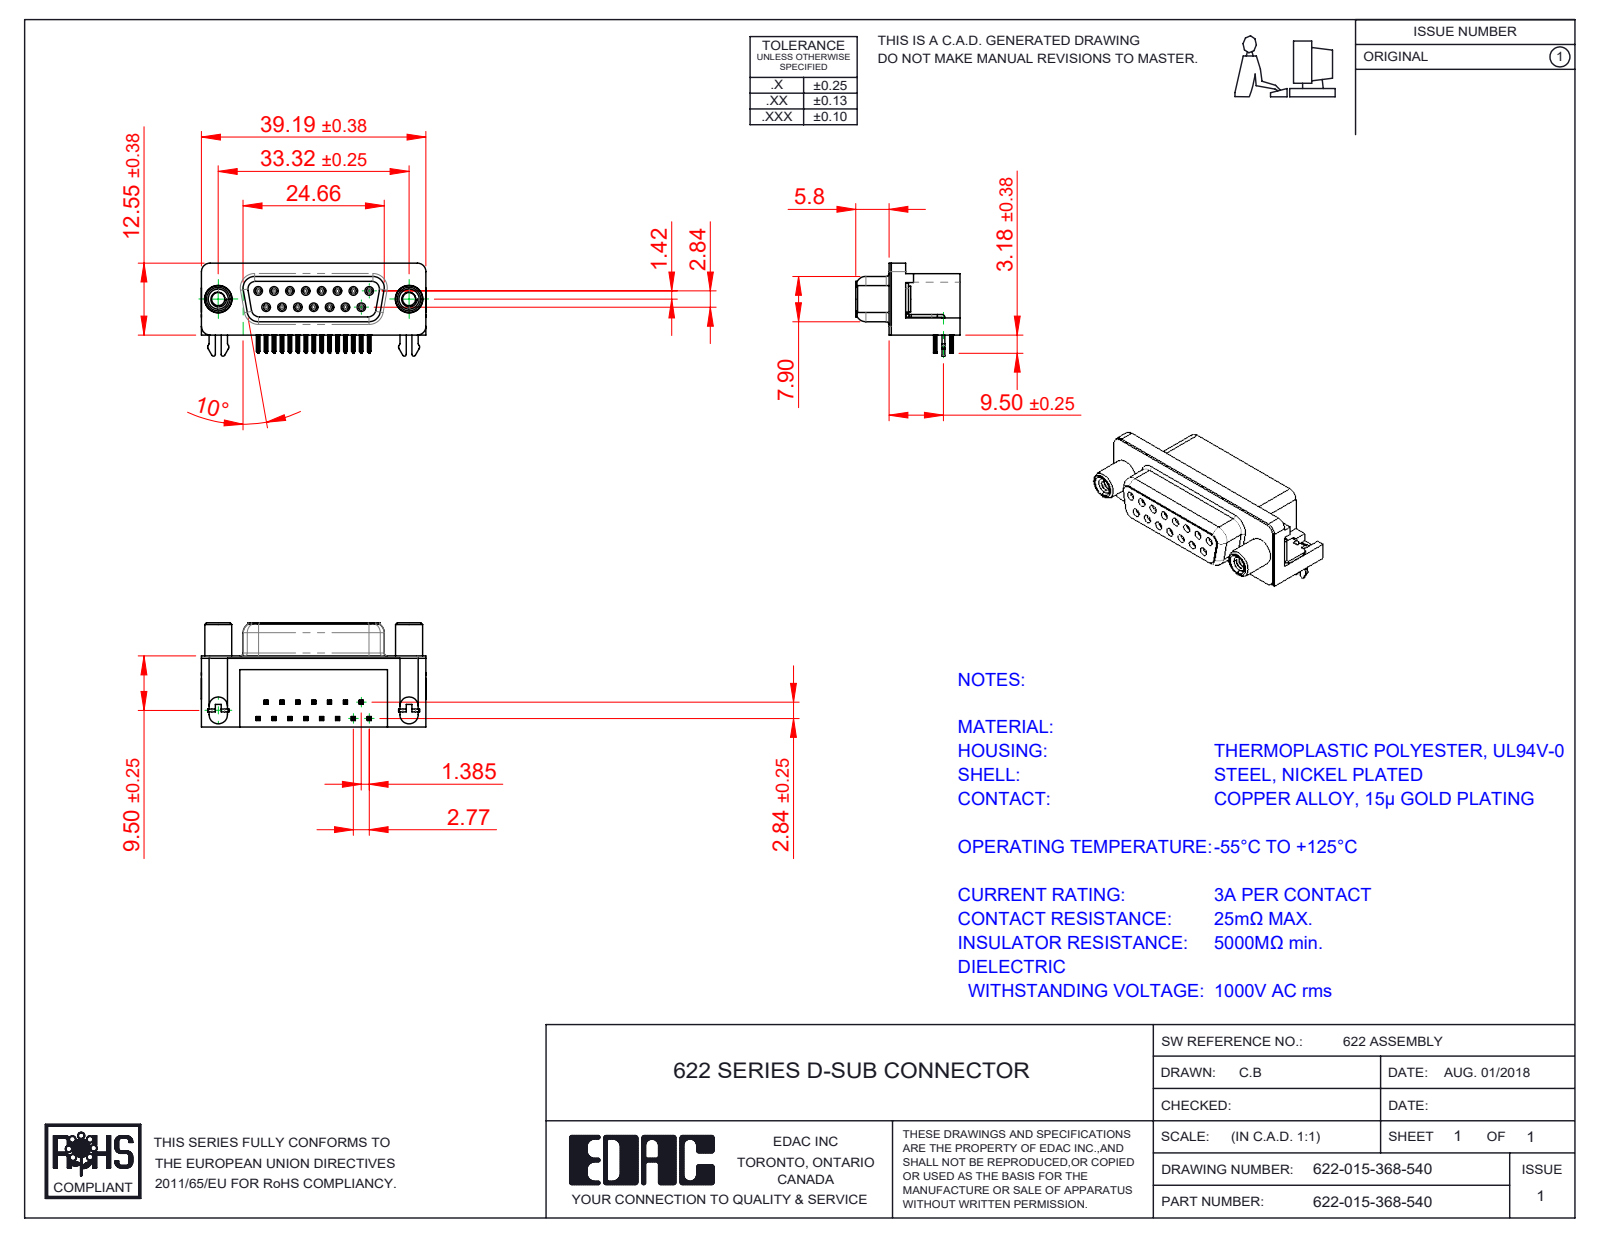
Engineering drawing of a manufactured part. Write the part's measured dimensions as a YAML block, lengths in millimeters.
part_name: "622-015-368-540; 622 Shell_15 Socket; 622 4 Prong Board Lock; 622 Round Threaded Standoff (+3 more)"
step_written_by: "SolidWorks 2016 (CONFIG_CONTROL_DESIGN)"
units: millimeters
bodies: {solids: 21, faces: 2541, planar: 1108, cylindrical: 619, other: 814}
overall_size: [39.22, 18.2, 16.25]
volume: 5288
surface_area: 6990
round_holes:
  - {diameter: 0.8, count: 15}
  - {diameter: 0.9, count: 15}
  - {diameter: 2, count: 2}
  - {diameter: 2.3, count: 2}
  - {diameter: 3.1, count: 2}
  - {diameter: 4, count: 2}
  - {diameter: 4.8, count: 2}
  - {diameter: 5, count: 2}
round_bosses_or_shafts:
  - {diameter: 1.2, count: 15}
  - {diameter: 4.9, count: 2}
  - {diameter: 4.7, count: 2}
  - {diameter: 4.5, count: 2}
  - {diameter: 3.85, count: 2}
  - {diameter: 3, count: 2}
partial_cylinders:
  - {radius: 0.1, count: 120}
  - {radius: 0.15, count: 60}
  - {radius: 0.35, count: 30}
  - {radius: 1, count: 18}
  - {radius: 0.34, count: 15}
  - {radius: 1.35, count: 8}
  - {radius: 1.5, count: 8}
  - {radius: 1.6, count: 8}
face_to_face_distances: [0.4, 12, 6.2, 10.35, 12.4, 2.9, 6.65, 0.85, 0.35, 5.8]
hole_center_spacings: [3.16, 2.77, 5.54, 8.31, 11.08, 5.03, 5.04, 7.48]
